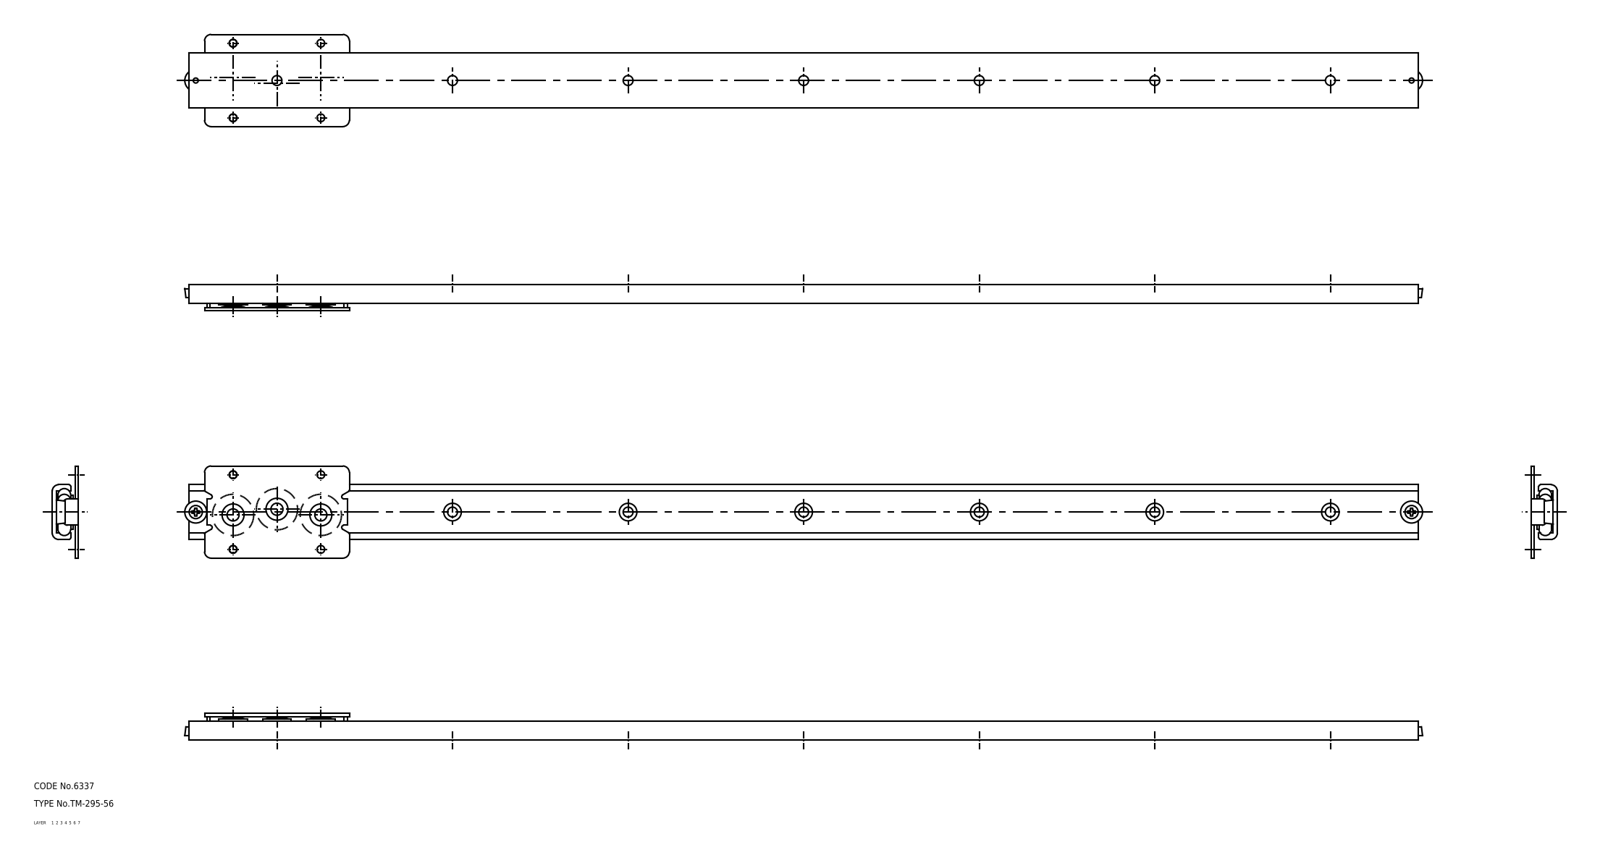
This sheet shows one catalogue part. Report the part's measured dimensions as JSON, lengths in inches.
{"part_name": "67122028; 67122041; 67122054; 67122067 (+3 more)", "step_written_by": "CADfix (AUTOMOTIVE_DESIGN)", "units": "inches", "bodies": {"solids": 7, "faces": 224, "planar": 0, "cylindrical": 0, "other": 224}, "overall_size": [22.205, 1.654, 0.472], "volume_in3": 3.092, "surface_area_in2": 82.13}
